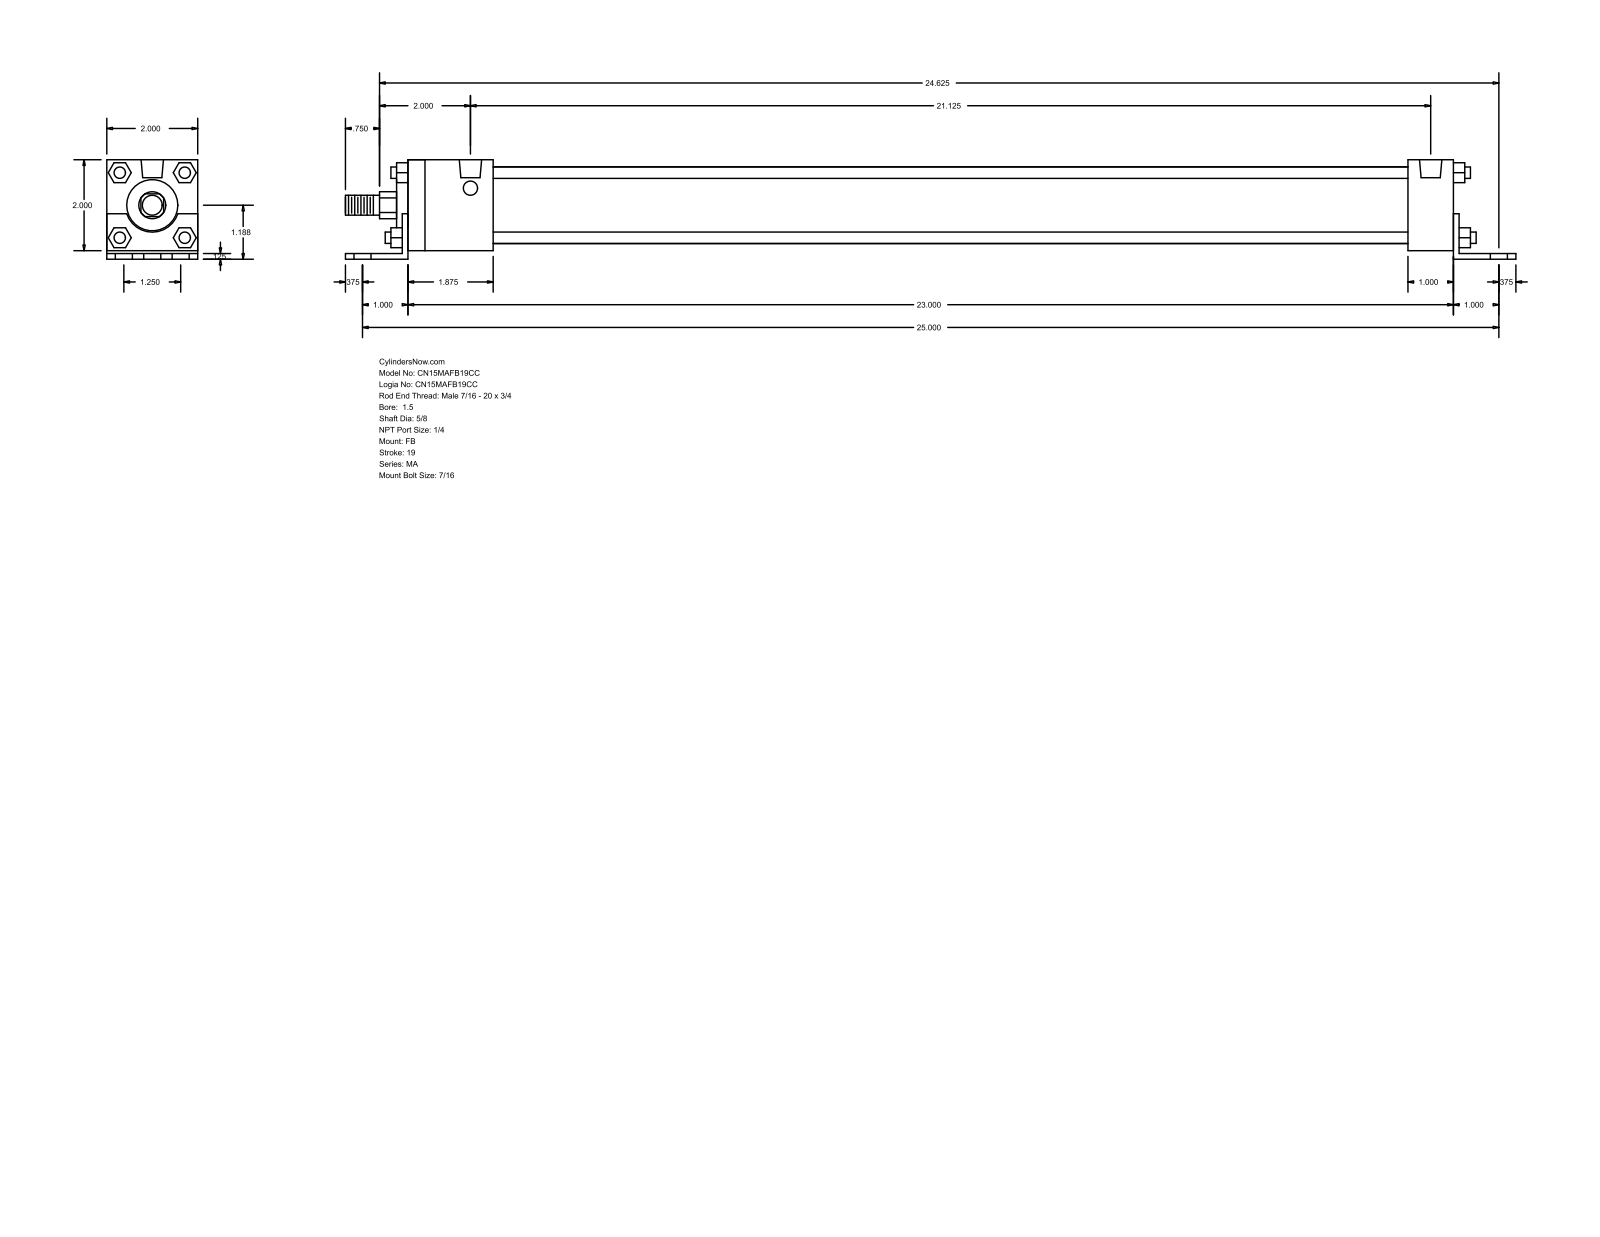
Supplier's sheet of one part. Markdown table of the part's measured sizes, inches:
| quantity | value |
| --- | --- |
| part name | MA_FB__0150_0.625 |
| STEP written by | GSSL Pune (CONFIG_CONTROL_DESIGN) |
| units | inches |
| bodies | 0 solids, 140 faces (105 planar, 35 cylindrical, 0 other) |
| overall size | 25.75 × 2.187 × 2 |
| round holes (diameter × count) | 0.437 × 6, 0.313 × 4, 0.492 × 2 |
| round bosses / shafts (diameter × count) | 0.25 × 4, 1.69 × 1, 1.125 × 1, 0.625 × 1, 0.437 × 1 |
| partial cylindrical surfaces (radius × count) | 0.297 × 1, 0.593 × 1 |
| main face-to-face distances | 2, 0.125, 0.187, 2.187, 0.063, 2.063, 1.125, 23.25, 23.375, 0.25 |
| hole center spacings | 0.625, 25.008, 25, 1.25, 1.625, 2.456, 21.125, 22.634 |
